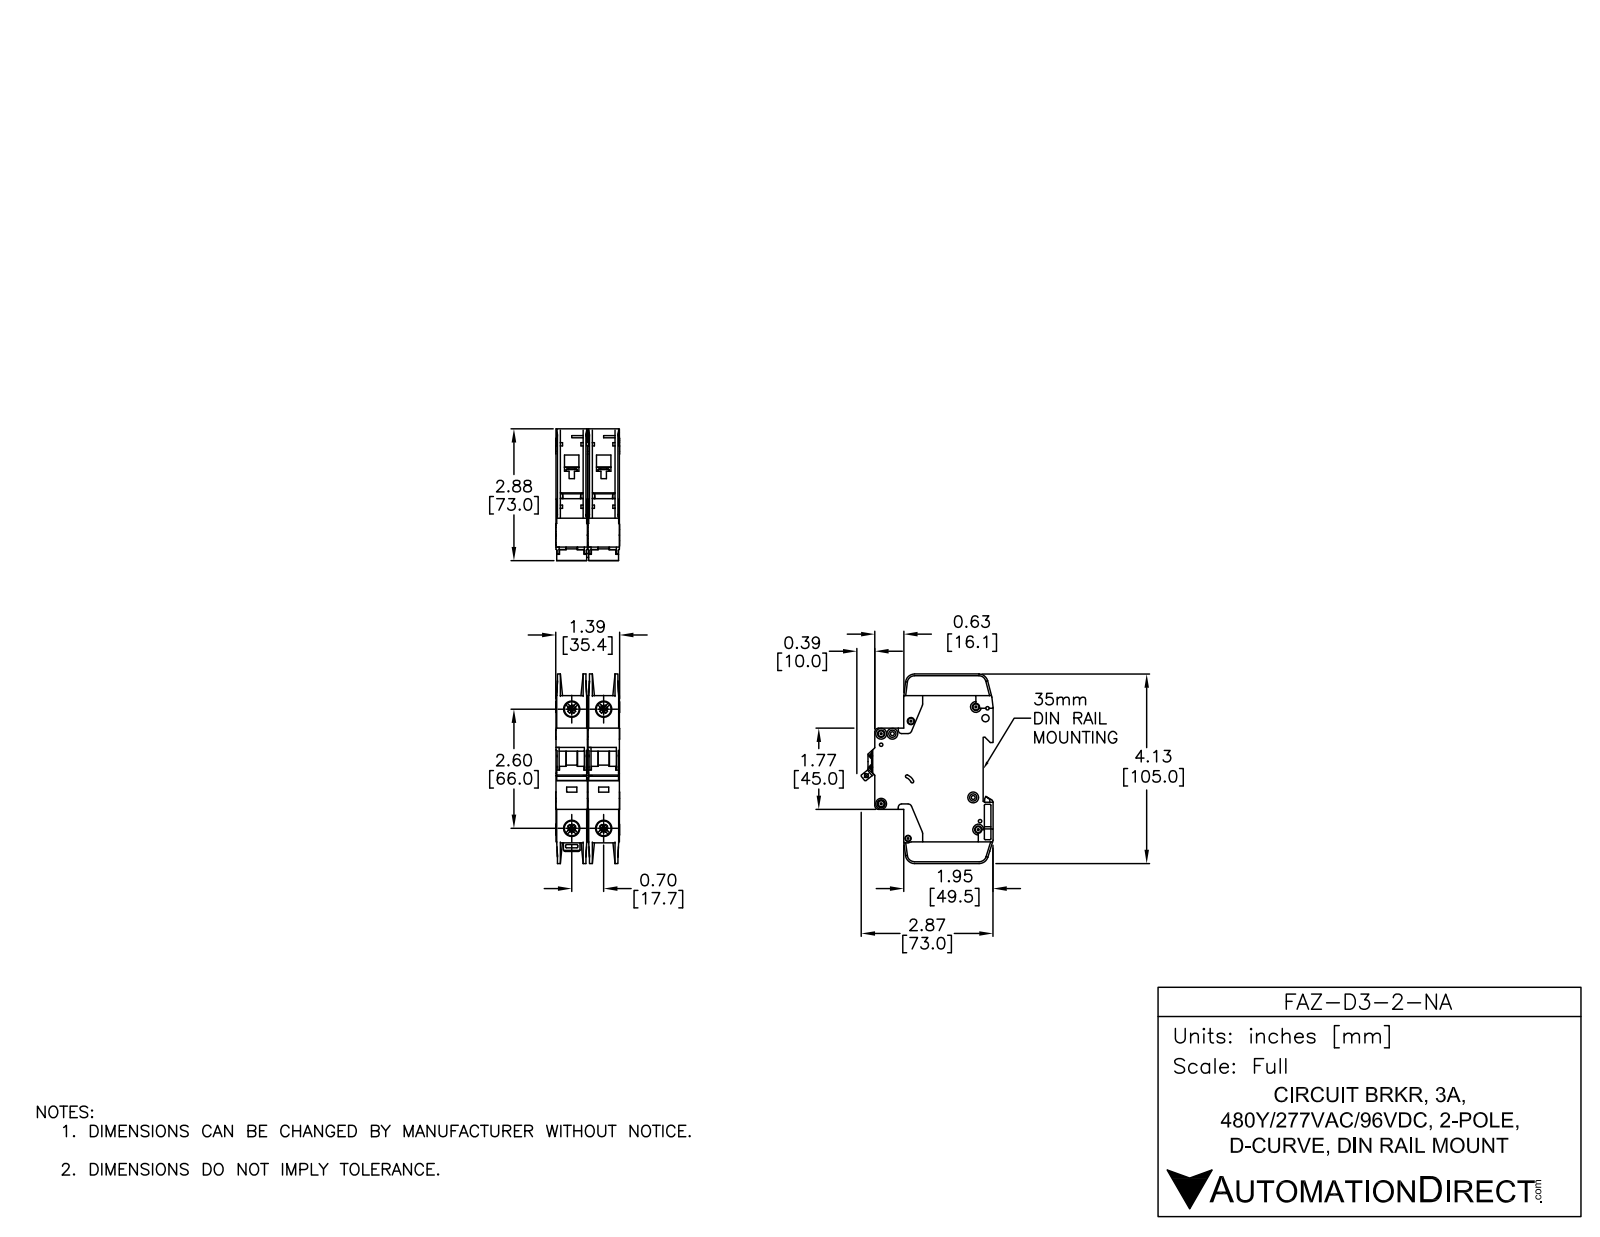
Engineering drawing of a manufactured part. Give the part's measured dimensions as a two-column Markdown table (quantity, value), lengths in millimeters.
| quantity | value |
| --- | --- |
| part name | FAZ-D3-2-NA |
| STEP written by | SolidWorks 2014 (AUTOMOTIVE_DESIGN) |
| units | millimeters |
| bodies | 6 solids, 1568 faces (818 planar, 526 cylindrical, 224 other) |
| overall size | 105 × 73.04 × 35.4 |
| volume | 155 390 mm³ |
| surface area | 49 479 mm² |
| round holes (diameter × count) | 3.6 × 7, 7.15 × 4, 8.2 × 4, 1.09 × 2, 1.5 × 2, 4 × 2, 1.9 × 1, 2.15 × 1, 2.2 × 1, 2.55 × 1, 3.3 × 1, 3.4 × 1 |
| round bosses / shafts (diameter × count) | 6 × 7, 2.5 × 2 |
| partial cylindrical surfaces (radius × count) | 0.25 × 47, 0.5 × 24, 1 × 18, 2 × 12, 5 × 5, 1.8 × 4, 4 × 4, 0.2 × 2 |
| main face-to-face distances | 17.7, 17.5, 0.7, 15.05, 2.45, 1.75, 15.75, 13.3, 35.2, 17 |
| hole center spacings | 6.2, 17.7, 66, 68.33, 5.19, 6.1, 8.19, 8.56 |
